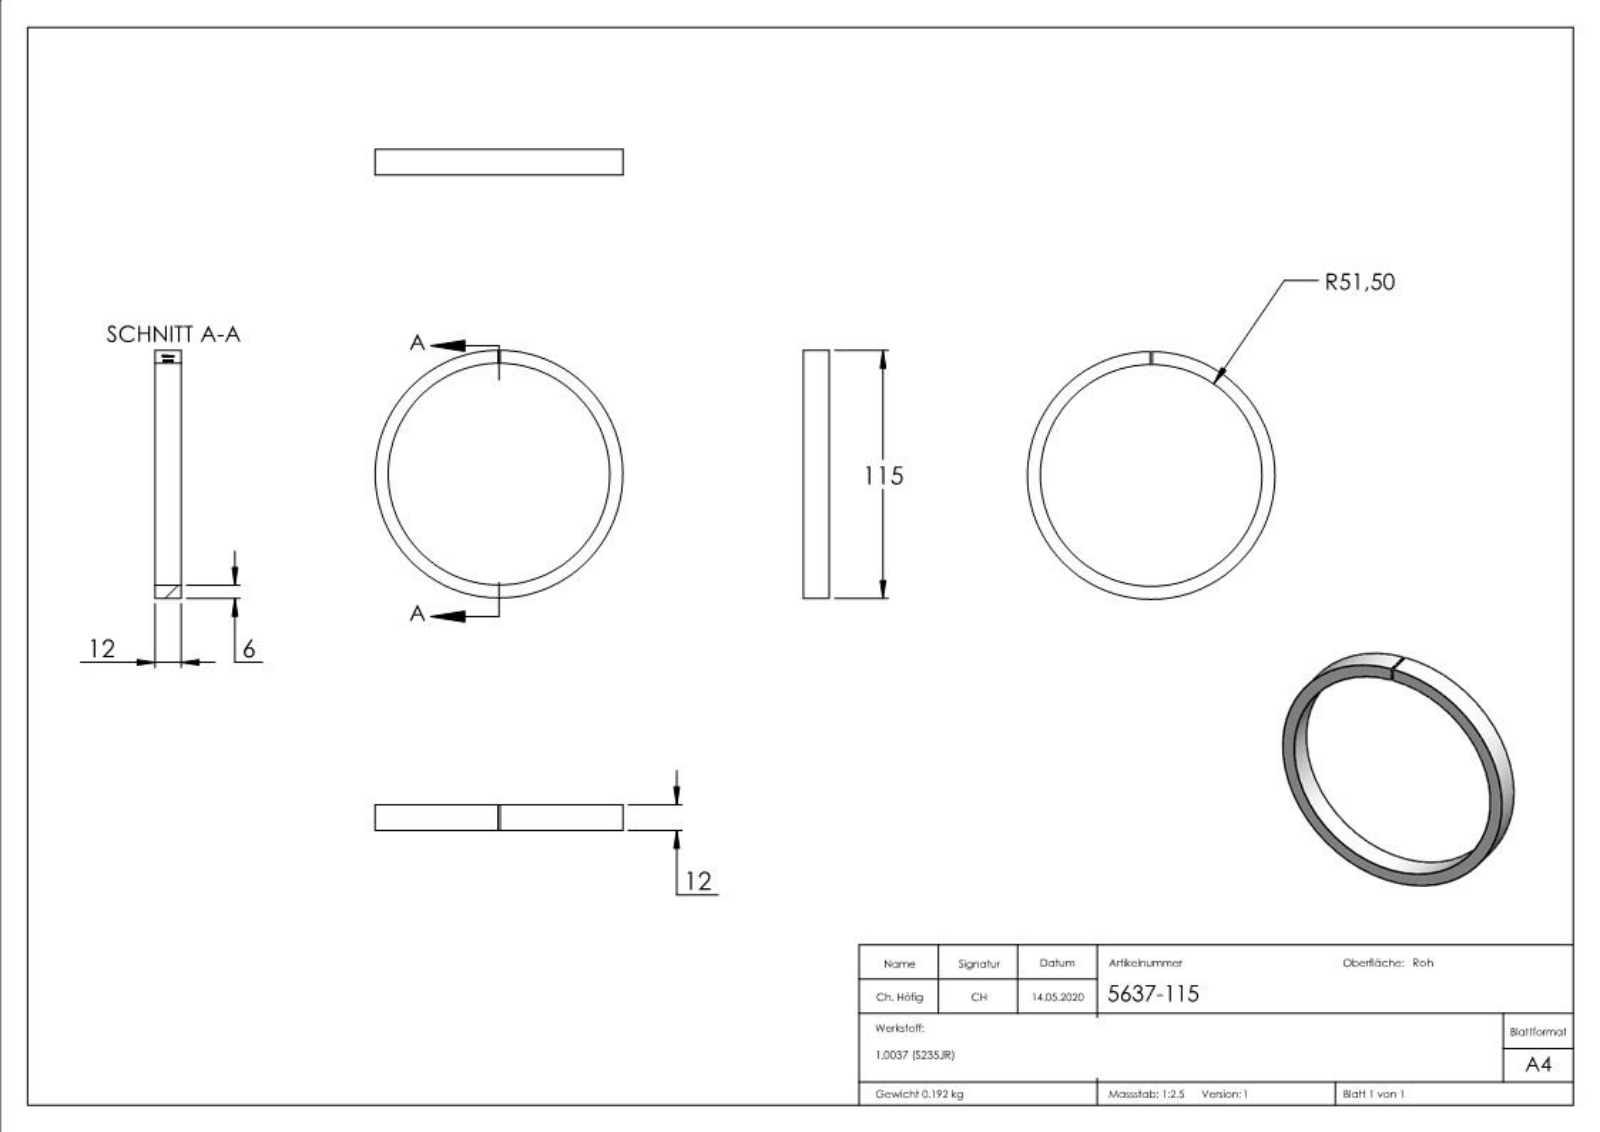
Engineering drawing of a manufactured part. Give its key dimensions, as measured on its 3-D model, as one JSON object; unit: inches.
{"part_name": "5637-115", "step_written_by": "SolidWorks 2015 (CONFIG_CONTROL_DESIGN)", "units": "inches", "bodies": {"solids": 1, "faces": 207, "planar": 118, "cylindrical": 2, "other": 87}, "overall_size": [4.528, 4.528, 0.472], "volume_in3": 1.5, "surface_area_in2": 19.28, "round_holes": [[4.055, 1]], "round_bosses_or_shafts": [[4.528, 1]], "face_to_face_distances": [0.472, 0.039, 0.043, 0.07, 0.033, 0.083, 0.078, 0.109, 0.048, 0.131]}
